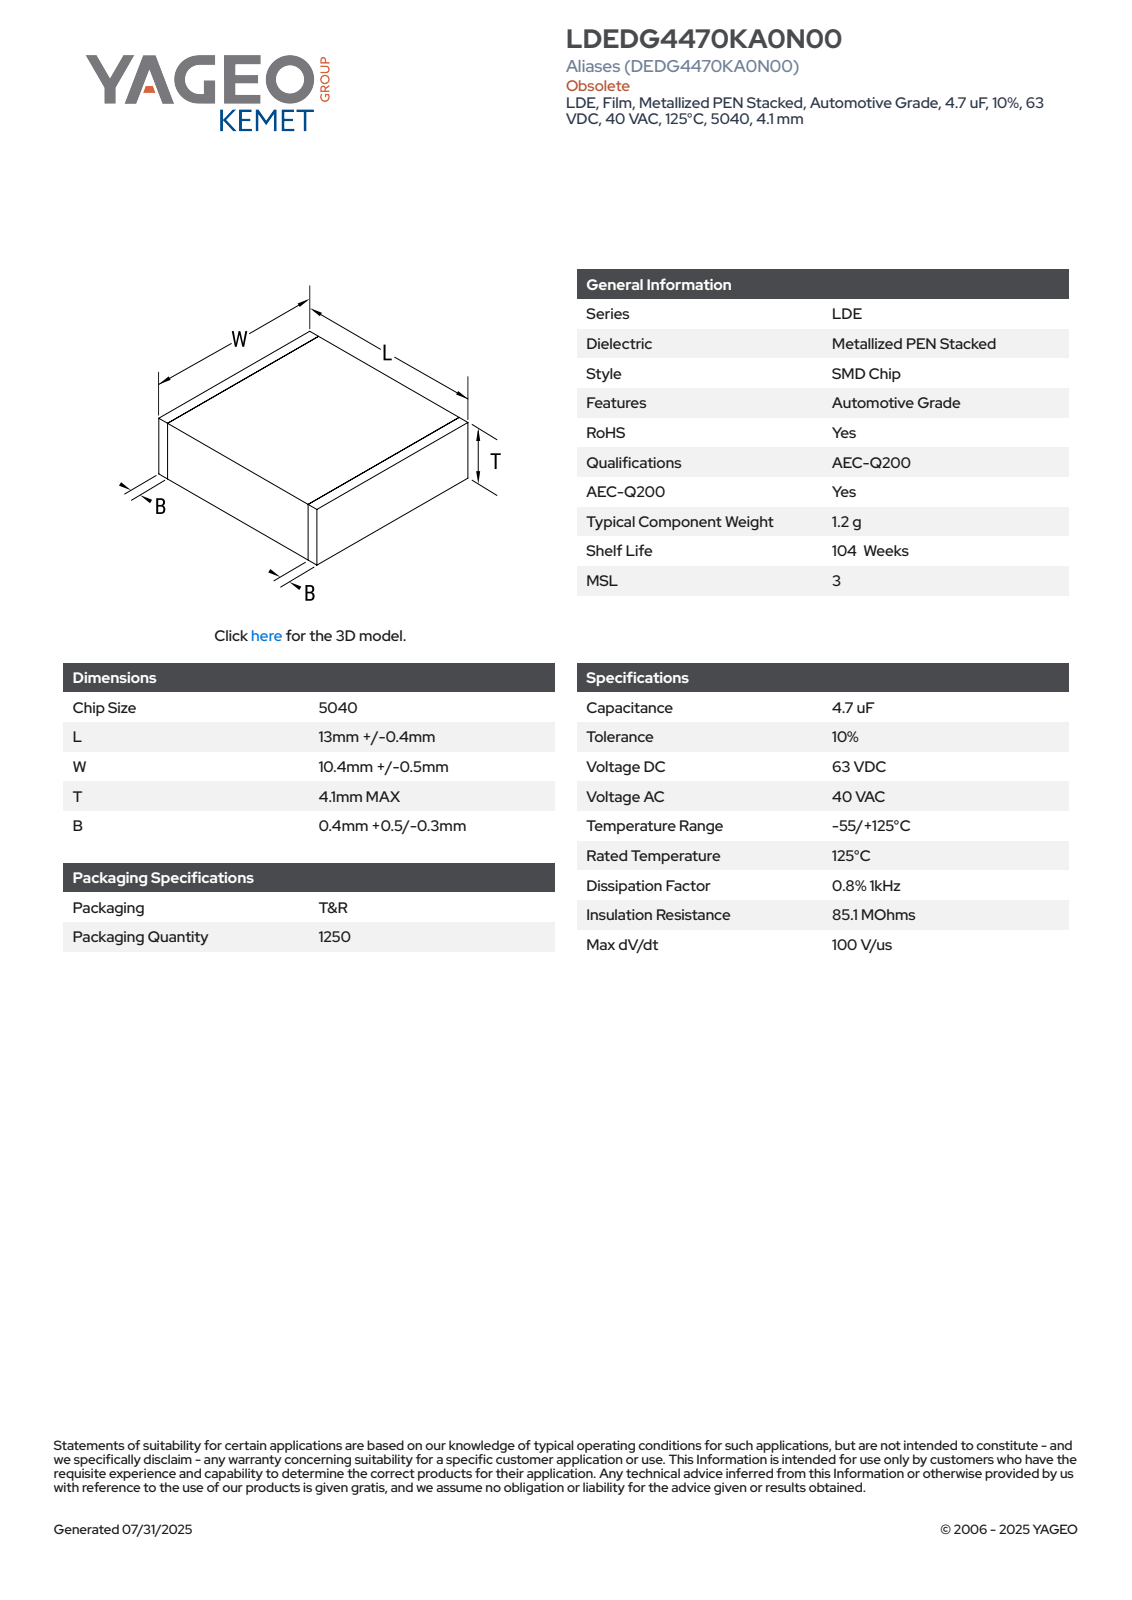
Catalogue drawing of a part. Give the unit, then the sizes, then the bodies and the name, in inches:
Units: inches
Overall size (bounding box): 0.528 × 0.429 × 0.161
Main face-to-face distances: 0.161, 0.428, 0.528, 0.161, 0.161, 0.429, 0.429, 0.02, 0.508, 0.488
Volume: 0.036 in³ · Surface area: 0.775 in²
Bodies: 4 solids, 73 faces (73 planar, 0 cylindrical, 0 other)
Part name (STEP PRODUCT): CFS_LDELDB_5040_L13.4W10.9T4.1B0.9
STEP written by: SolidWorks 2020 (AUTOMOTIVE_DESIGN)
